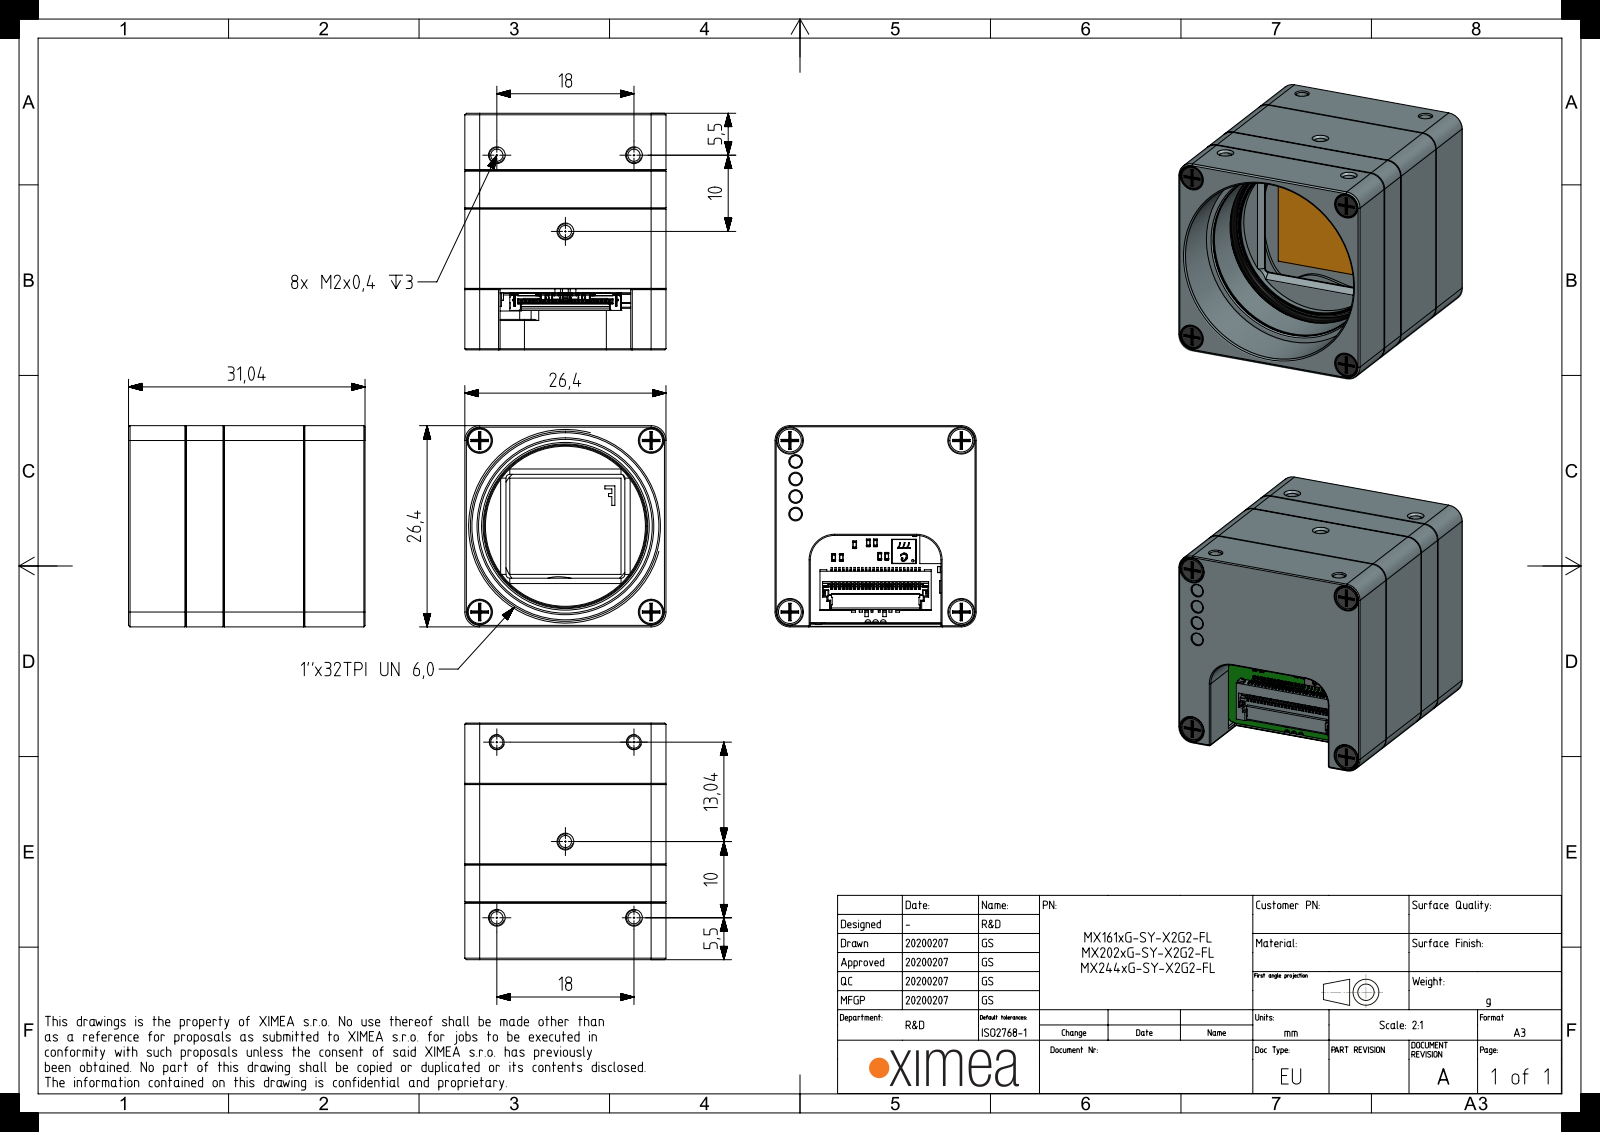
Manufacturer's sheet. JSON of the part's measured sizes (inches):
{"part_name": "MX-X2G2-MAIN-FL-PCA-LW; MECH-MX-THERMAL-PAD-10X10; SROB-M2x10-CUST; MECH-LIGHTPIPE-1.63x4.14 (+8 more)", "step_written_by": "SIEMENS PLM Software NX 1907 (AUTOMOTIVE_DESIGN)", "units": "inches", "bodies": {"solids": 31, "faces": 7075, "planar": 5062, "cylindrical": 1751, "other": 262}, "overall_size": [1.222, 1.039, 1.039], "volume_in3": 0.627, "surface_area_in2": 26.85, "round_holes": [[0.063, 13], [0.035, 4], [0.079, 4], [0.083, 4], [0.118, 4], [0.126, 4], [0.132, 4], [0.051, 2], [0.067, 2], [0.827, 1], [0.898, 1], [0.961, 1]], "round_bosses_or_shafts": [[0.075, 4], [0.064, 4], [0.033, 4], [0.118, 2], [0.063, 2], [0.984, 1], [0.85, 1]], "partial_cylinders_radius": [[0.015, 18], [0.013, 17], [0.059, 15], [0.006, 14], [0.02, 12], [0.039, 12], [0.008, 10], [0.01, 8]], "face_to_face_distances": [1.039, 0.039, 0.458, 0.142, 0.317, 0.102, 0.419, 0.415, 0.04, 0.181], "hole_center_spacings": [0.626, 0.886, 0.091, 0.148, 0.181, 0.53, 0.531, 0.624]}
